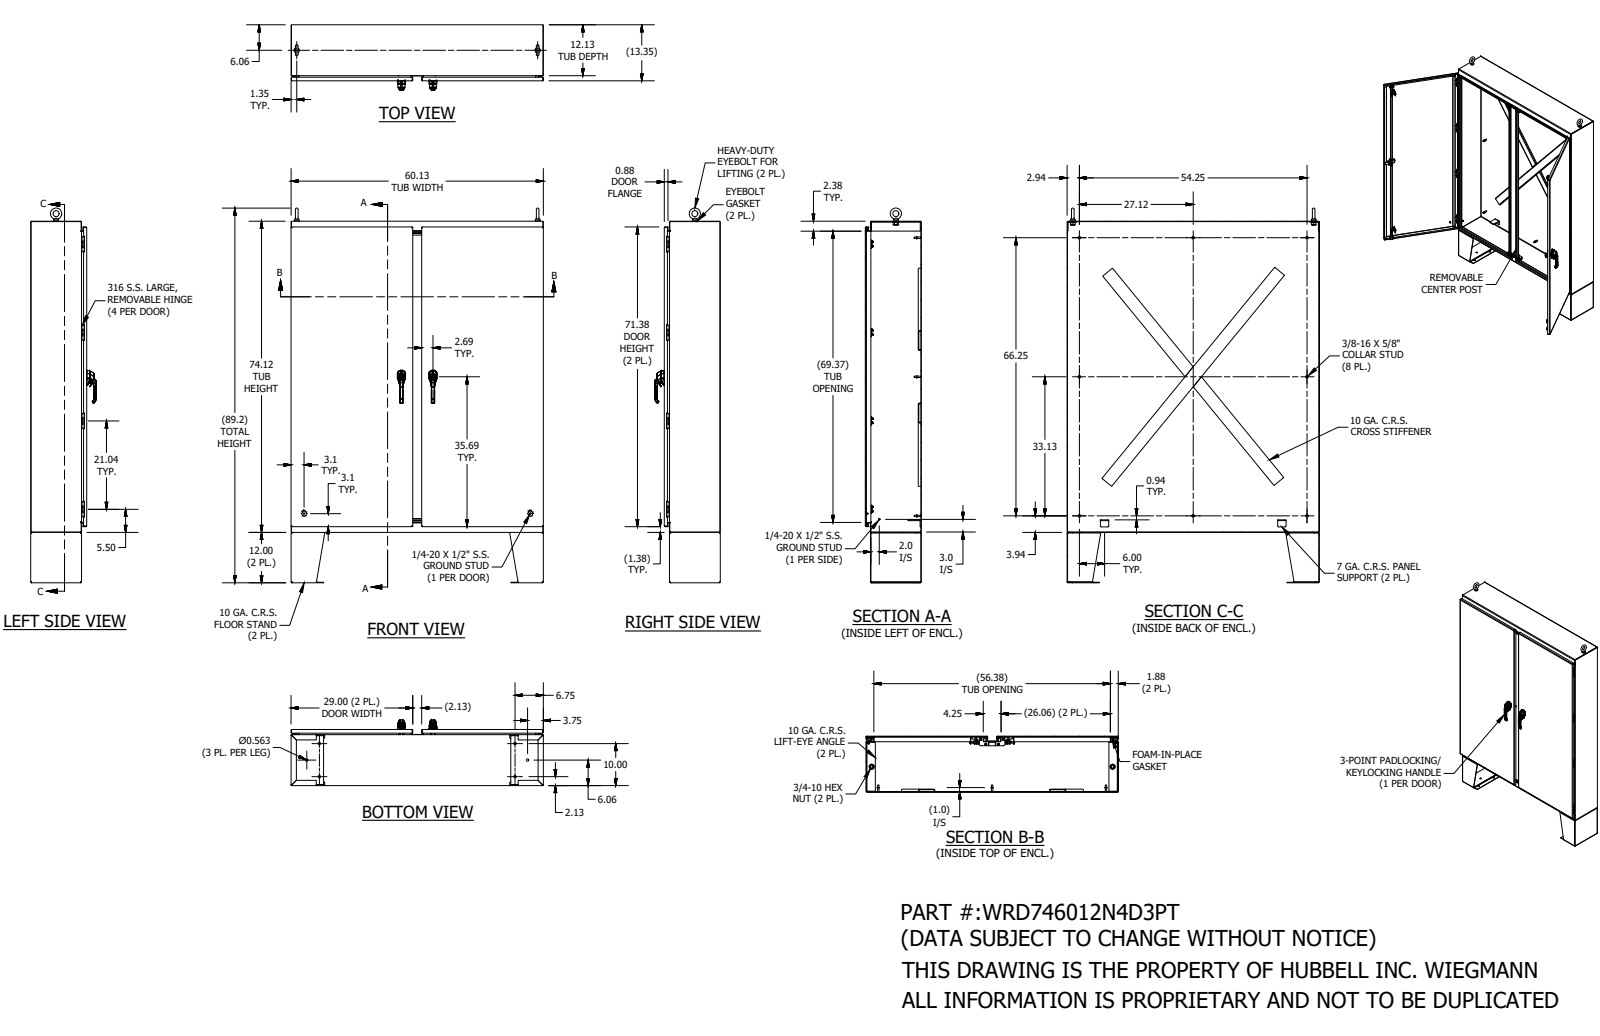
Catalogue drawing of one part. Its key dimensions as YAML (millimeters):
part_name: "WRD746012N4D3PT_REV1"
step_written_by: "SolidWorks 2021 (AUTOMOTIVE_DESIGN)"
units: millimeters
bodies: {solids: 103, faces: 4949, planar: 1916, cylindrical: 1719, other: 1314}
overall_size: [2266.9, 1527.4, 396.2]
volume: 29300000
surface_area: 20810000
round_holes:
  - {diameter: 6.8, count: 20}
  - {diameter: 14.3, count: 18}
  - {diameter: 7.5, count: 16}
  - {diameter: 16.5, count: 16}
  - {diameter: 5.1, count: 8}
  - {diameter: 7, count: 8}
  - {diameter: 5.4, count: 6}
  - {diameter: 7.1, count: 6}
  - {diameter: 3.1, count: 4}
  - {diameter: 4, count: 4}
  - {diameter: 5.1, count: 4}
  - {diameter: 6.1, count: 4}
round_bosses_or_shafts:
  - {diameter: 6.4, count: 10}
  - {diameter: 15.9, count: 8}
  - {diameter: 8.4, count: 8}
  - {diameter: 34, count: 2}
  - {diameter: 28.4, count: 2}
  - {diameter: 28, count: 2}
  - {diameter: 25.8, count: 2}
  - {diameter: 25.4, count: 2}
partial_cylinders:
  - {radius: 0.5, count: 375}
  - {radius: 0.3, count: 99}
  - {radius: 2.4, count: 48}
  - {radius: 0.5, count: 44}
  - {radius: 3, count: 34}
  - {radius: 3.2, count: 32}
  - {radius: 2, count: 30}
  - {radius: 1.3, count: 28}
face_to_face_distances: [2.6, 336.4, 333.8, 2.6, 339.1, 336.4, 1524.5, 305.3, 1880.1, 1527.2]
hole_center_spacings: [534.5, 1588.1, 25.4, 1068.9, 1495.4, 1495.6, 1838.2, 509.1]
